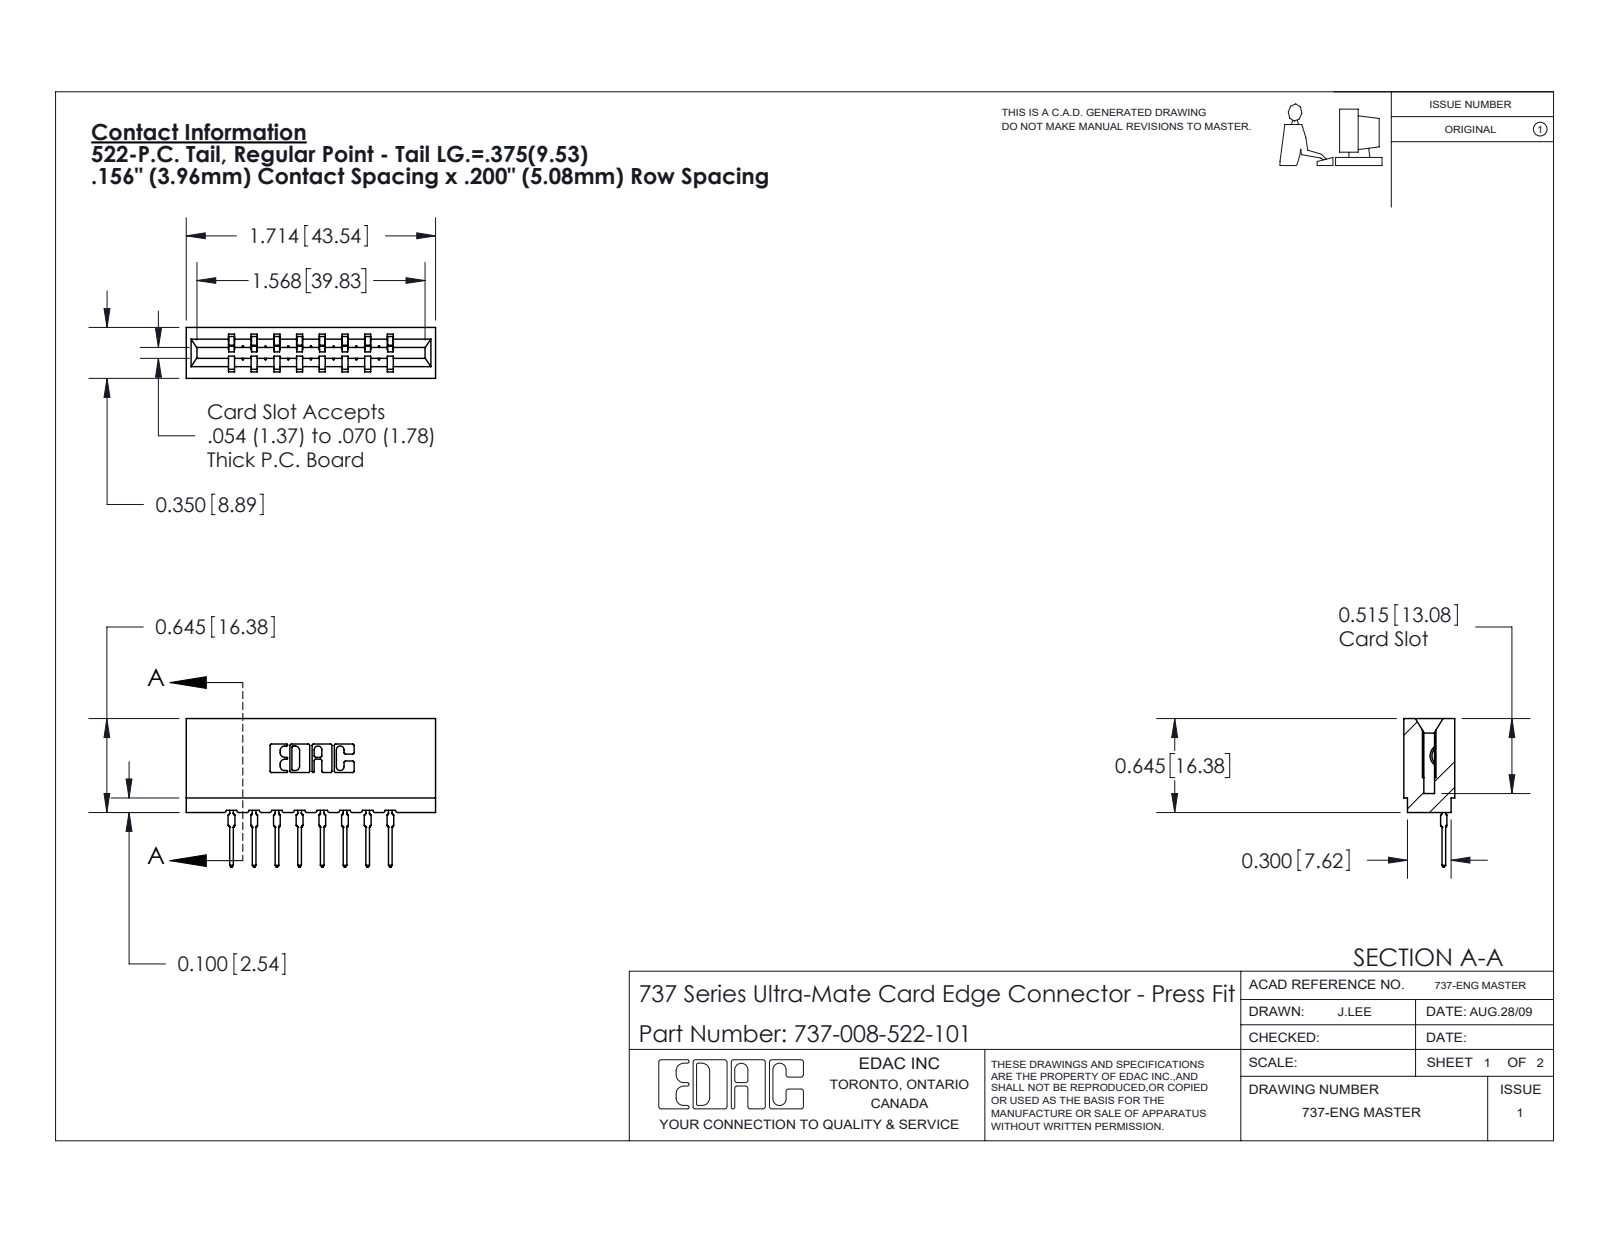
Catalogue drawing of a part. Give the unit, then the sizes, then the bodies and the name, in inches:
Units: inches
Overall size (bounding box): 1.714 × 1.021 × 0.35
Partial cylindrical surfaces — rounded edges, fillets, slot ends (radius × count): R0.01 ×22, R0.015 ×16, R0.021 ×16, R0.007 ×6, R0.031 ×6, R0.005 ×4, R0.011 ×4, R0.026 ×3
Main face-to-face distances: 0.156, 0.138, 0.212, 0.35, 0.624, 0.312, 0.354, 0.198, 0.468, 0.78
Volume: 0.272 in³ · Surface area: 8.321 in²
Bodies: 9 solids, 998 faces (598 planar, 192 cylindrical, 208 other)
Part name (STEP PRODUCT): 745-292-001_522; 737-008-522-101; 737 Part_Insulator Option - 01
STEP written by: SolidWorks 2020 (CONFIG_CONTROL_DESIGN)
